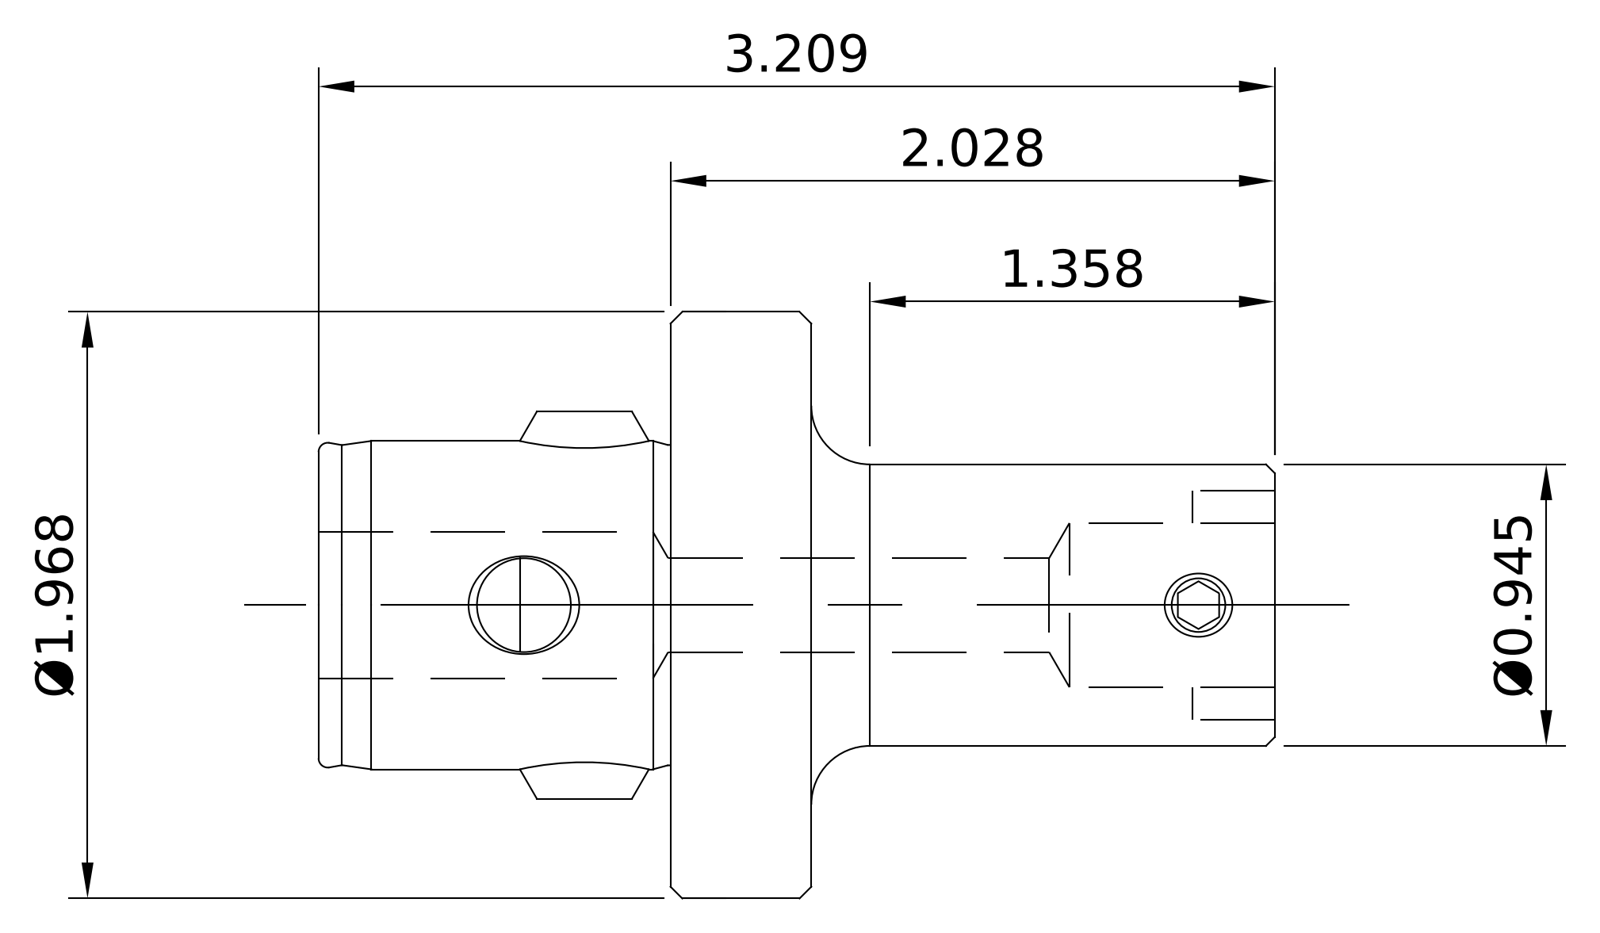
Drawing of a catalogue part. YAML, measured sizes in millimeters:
part_name: "10.332.52X_11.332.521; 11.332.521; 10.691.50X_10.691.505; 691-50XRing_10.691.505Ring (+1 more)"
step_written_by: "SolidWorks 2016 (CONFIG_CONTROL_DESIGN)"
units: millimeters
bodies: {solids: 4, faces: 96, planar: 42, cylindrical: 25, other: 29}
overall_size: [81.5, 50, 50]
volume: 51164
surface_area: 16049
round_holes:
  - {diameter: 4.2, count: 1}
  - {diameter: 4.5, count: 1}
  - {diameter: 5.2, count: 1}
  - {diameter: 8, count: 1}
  - {diameter: 8.8, count: 1}
  - {diameter: 10, count: 1}
  - {diameter: 11, count: 1}
  - {diameter: 12.5, count: 1}
  - {diameter: 14, count: 1}
  - {diameter: 14.5, count: 1}
round_bosses_or_shafts:
  - {diameter: 50, count: 1}
  - {diameter: 28, count: 1}
  - {diameter: 24, count: 1}
  - {diameter: 10.9, count: 1}
  - {diameter: 6.9, count: 1}
  - {diameter: 5, count: 1}
partial_cylinders:
  - {radius: 2, count: 2}
  - {radius: 14, count: 1}
face_to_face_distances: [12, 30, 42, 39.5, 81.5, 51.5, 4, 22, 18, 11]
hole_center_spacings: [10.5, 57.45]
